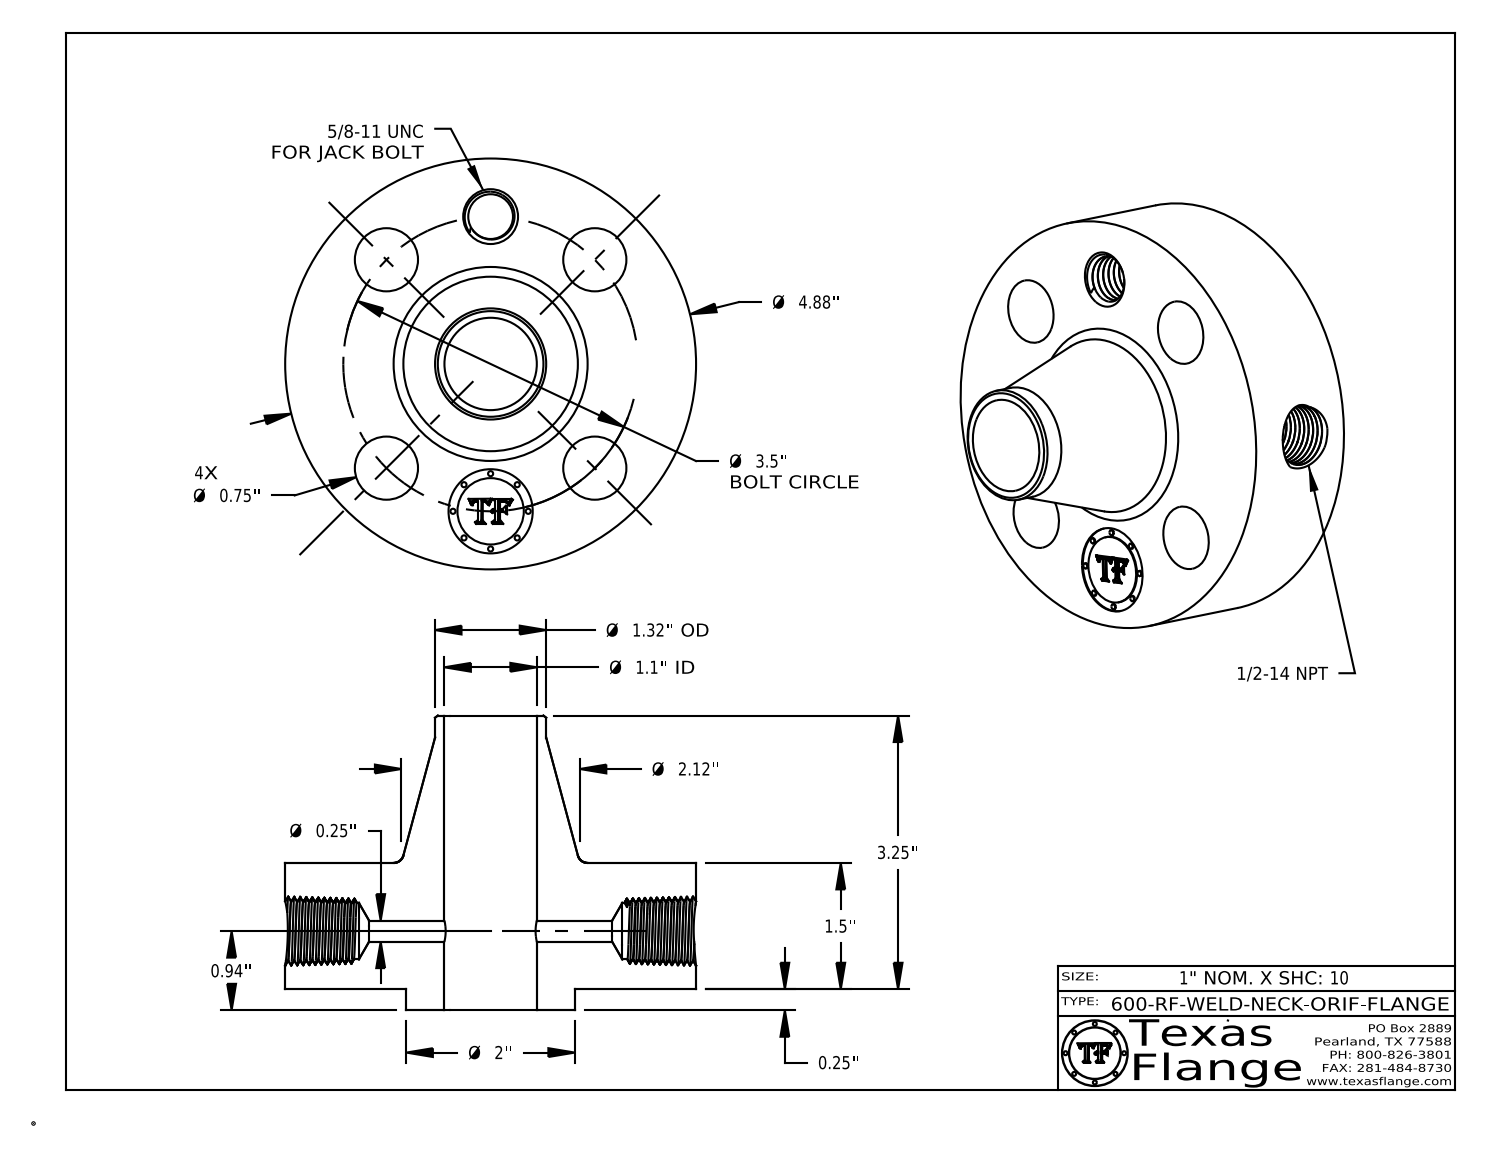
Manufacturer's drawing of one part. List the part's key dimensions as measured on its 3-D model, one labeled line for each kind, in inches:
Part name (STEP PRODUCT): 600-RF-WELD-NECK
STEP written by: CATIA V5 STEP AP214 (AUTOMOTIVE_DESIGN)
Units: inches
Bodies: 1 solid, 764 faces (369 planar, 87 cylindrical, 308 other)
Overall size (bounding box): 4.88 × 4.88 × 3.5
Volume: 25.5 in³ · Surface area: 101.5 in²
Round holes (diameter × count): ⌀0.75 ×4, ⌀0.25 ×1, ⌀0.531 ×1, ⌀0.672 ×1, ⌀1 ×1, ⌀1.097 ×1
Round bosses / shafts (diameter × count): ⌀0.061 ×8, ⌀4.88 ×1, ⌀2 ×1, ⌀1.32 ×1, ⌀0.788 ×1
Main face-to-face distances: 1.5, 1.75, 0.25, 1.735, 1.485, 0.015, 3.5, 3.25, 1.765, 0.298
Hole centre spacings: 1.75, 1.339, 2.475, 3.233, 3.5
